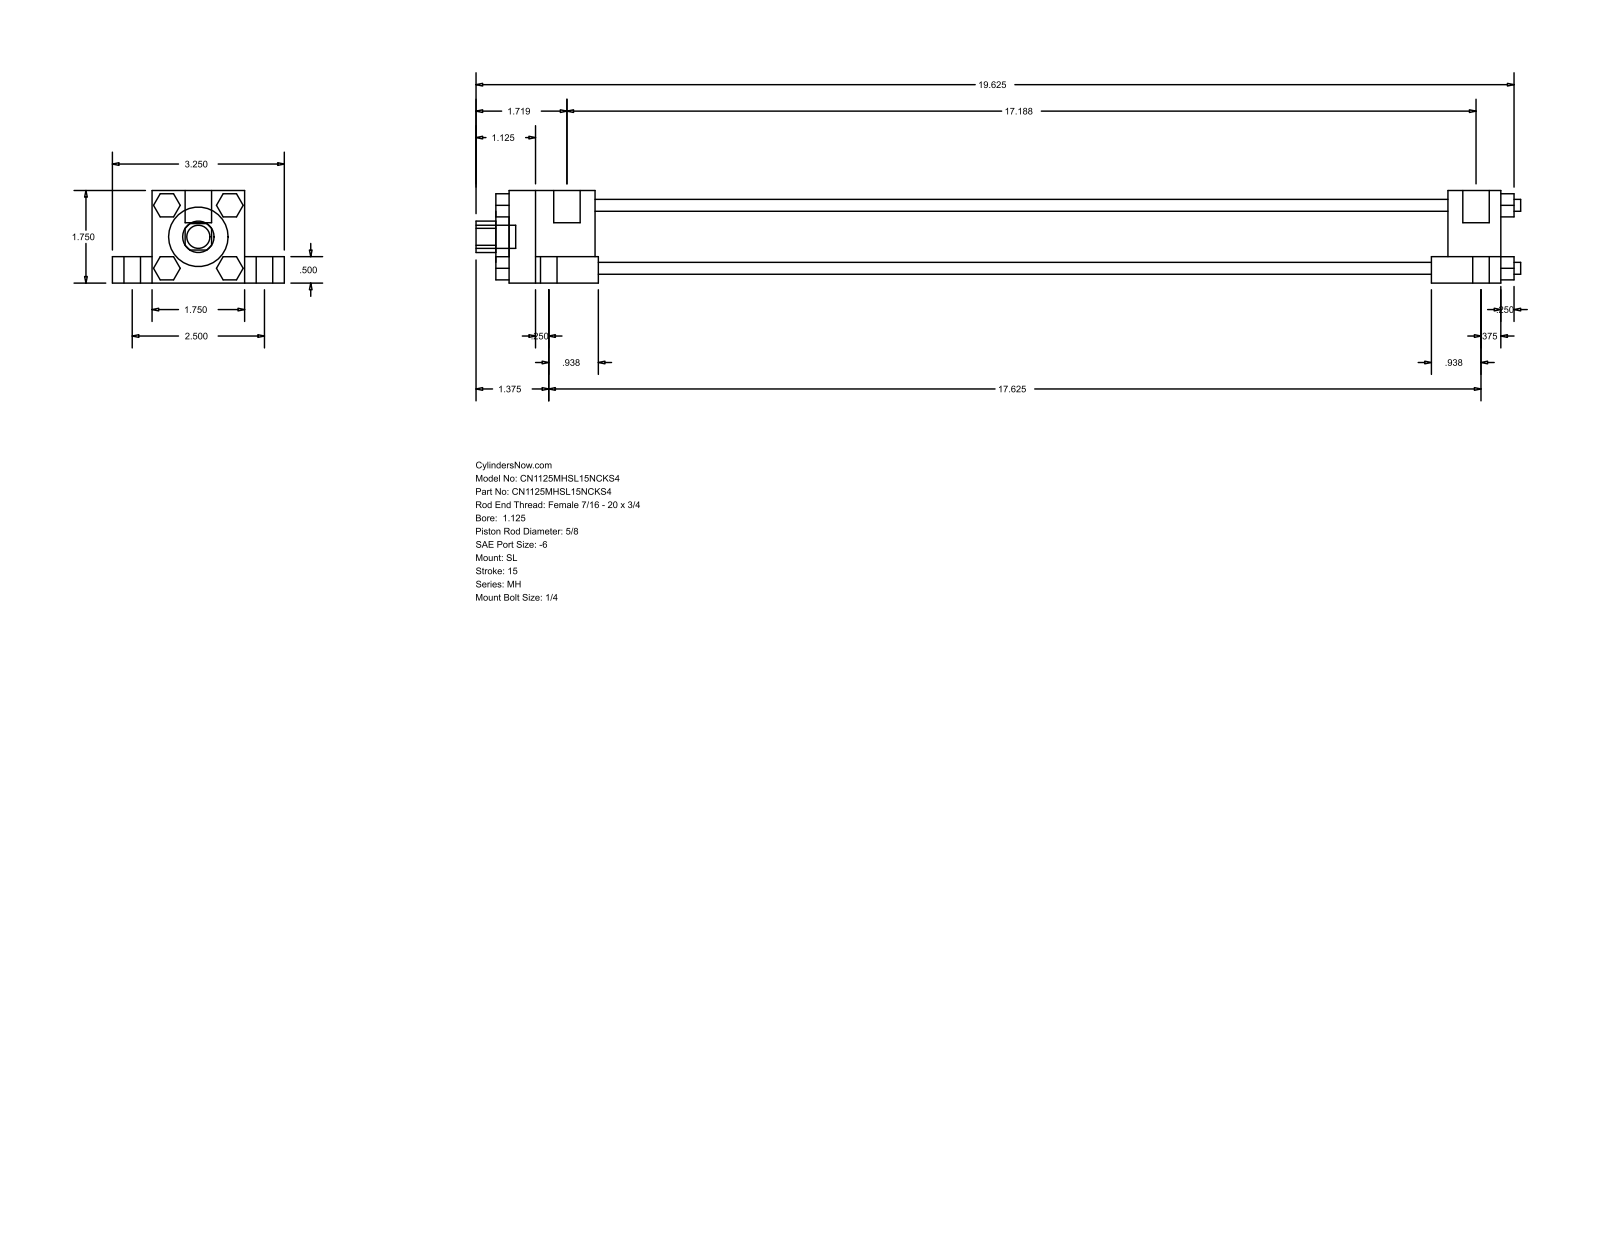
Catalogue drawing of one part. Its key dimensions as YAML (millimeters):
part_name: "MH_SL__0112_0.625"
step_written_by: "GSSL Pune (CONFIG_CONTROL_DESIGN)"
units: millimeters
bodies: {solids: 0, faces: 150, planar: 114, cylindrical: 36, other: 0}
overall_size: [501.65, 82.55, 44.45]
round_holes:
  - {diameter: 15.88, count: 1}
  - {diameter: 28.57, count: 1}
  - {diameter: 34.92, count: 1}
round_bosses_or_shafts:
  - {diameter: 14.29, count: 4}
  - {diameter: 7.94, count: 4}
  - {diameter: 5.71, count: 4}
  - {diameter: 5.56, count: 4}
  - {diameter: 12.7, count: 2}
  - {diameter: 11.11, count: 1}
partial_cylinders:
  - {radius: 7.54, count: 1}
face_to_face_distances: [44.46, 19.04, 12.7, 31.76, 63.5, 11.11, 409.58, 434.97, 25.39, 41.27]
